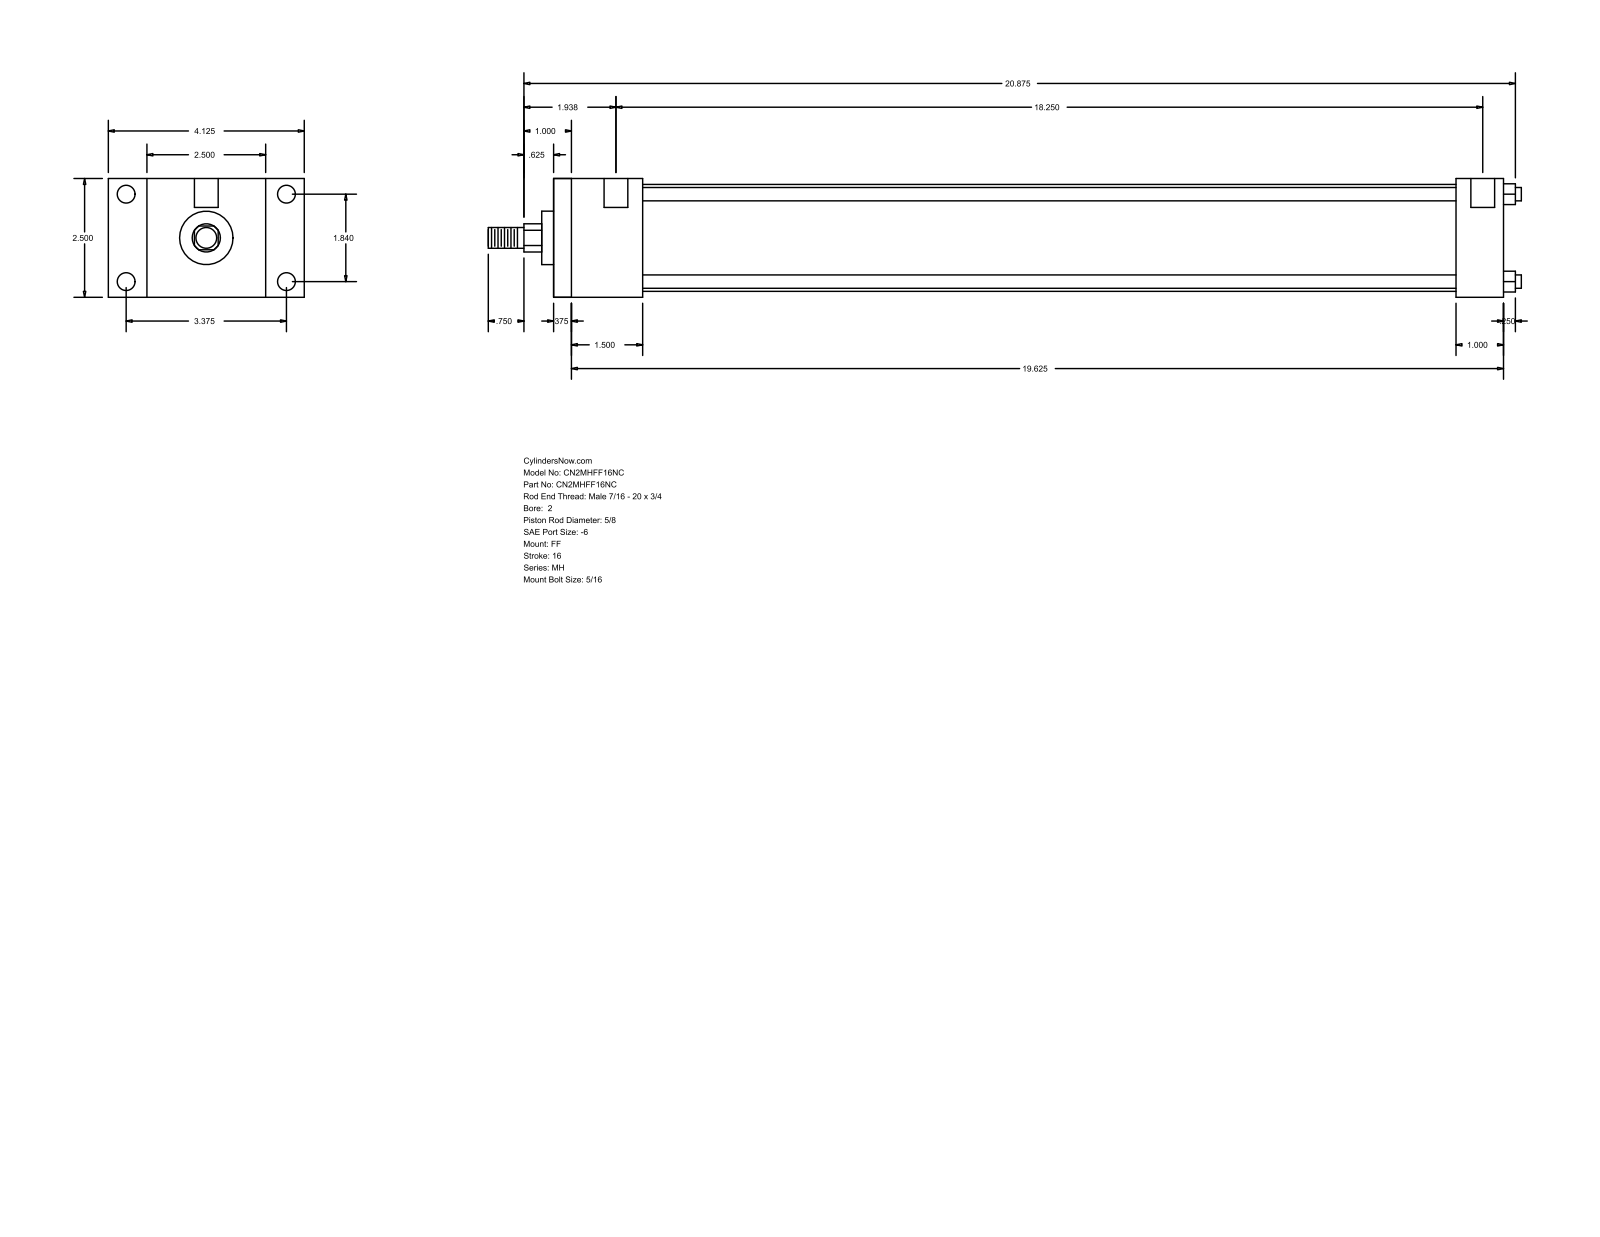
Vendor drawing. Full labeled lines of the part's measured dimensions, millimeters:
Part name (STEP PRODUCT): MH_FF__0200_0.625
STEP written by: GSSL Pune (CONFIG_CONTROL_DESIGN)
Units: millimetres
Bodies: 0 solids, 92 faces (64 planar, 28 cylindrical, 0 other)
Overall size (bounding box): 552.45 × 104.78 × 63.5
Round holes (diameter × count): ⌀5.56 ×4, ⌀9.53 ×4, ⌀12.7 ×2
Round bosses / shafts (diameter × count): ⌀7.14 ×4, ⌀57.15 ×1, ⌀28.57 ×1, ⌀15.88 ×1, ⌀11.11 ×1
Partial cylindrical surfaces — rounded edges, fillets, slot ends (radius × count): R7.54 ×1
Main face-to-face distances: 63.5, 508, 9.52, 498.48, 25.4, 38.1, 47.62, 482.6, 473.08, 434.98
Hole centre spacings: 46.74, 85.72, 97.63, 471.49, 3.18, 4.76, 463.55, 466.73
